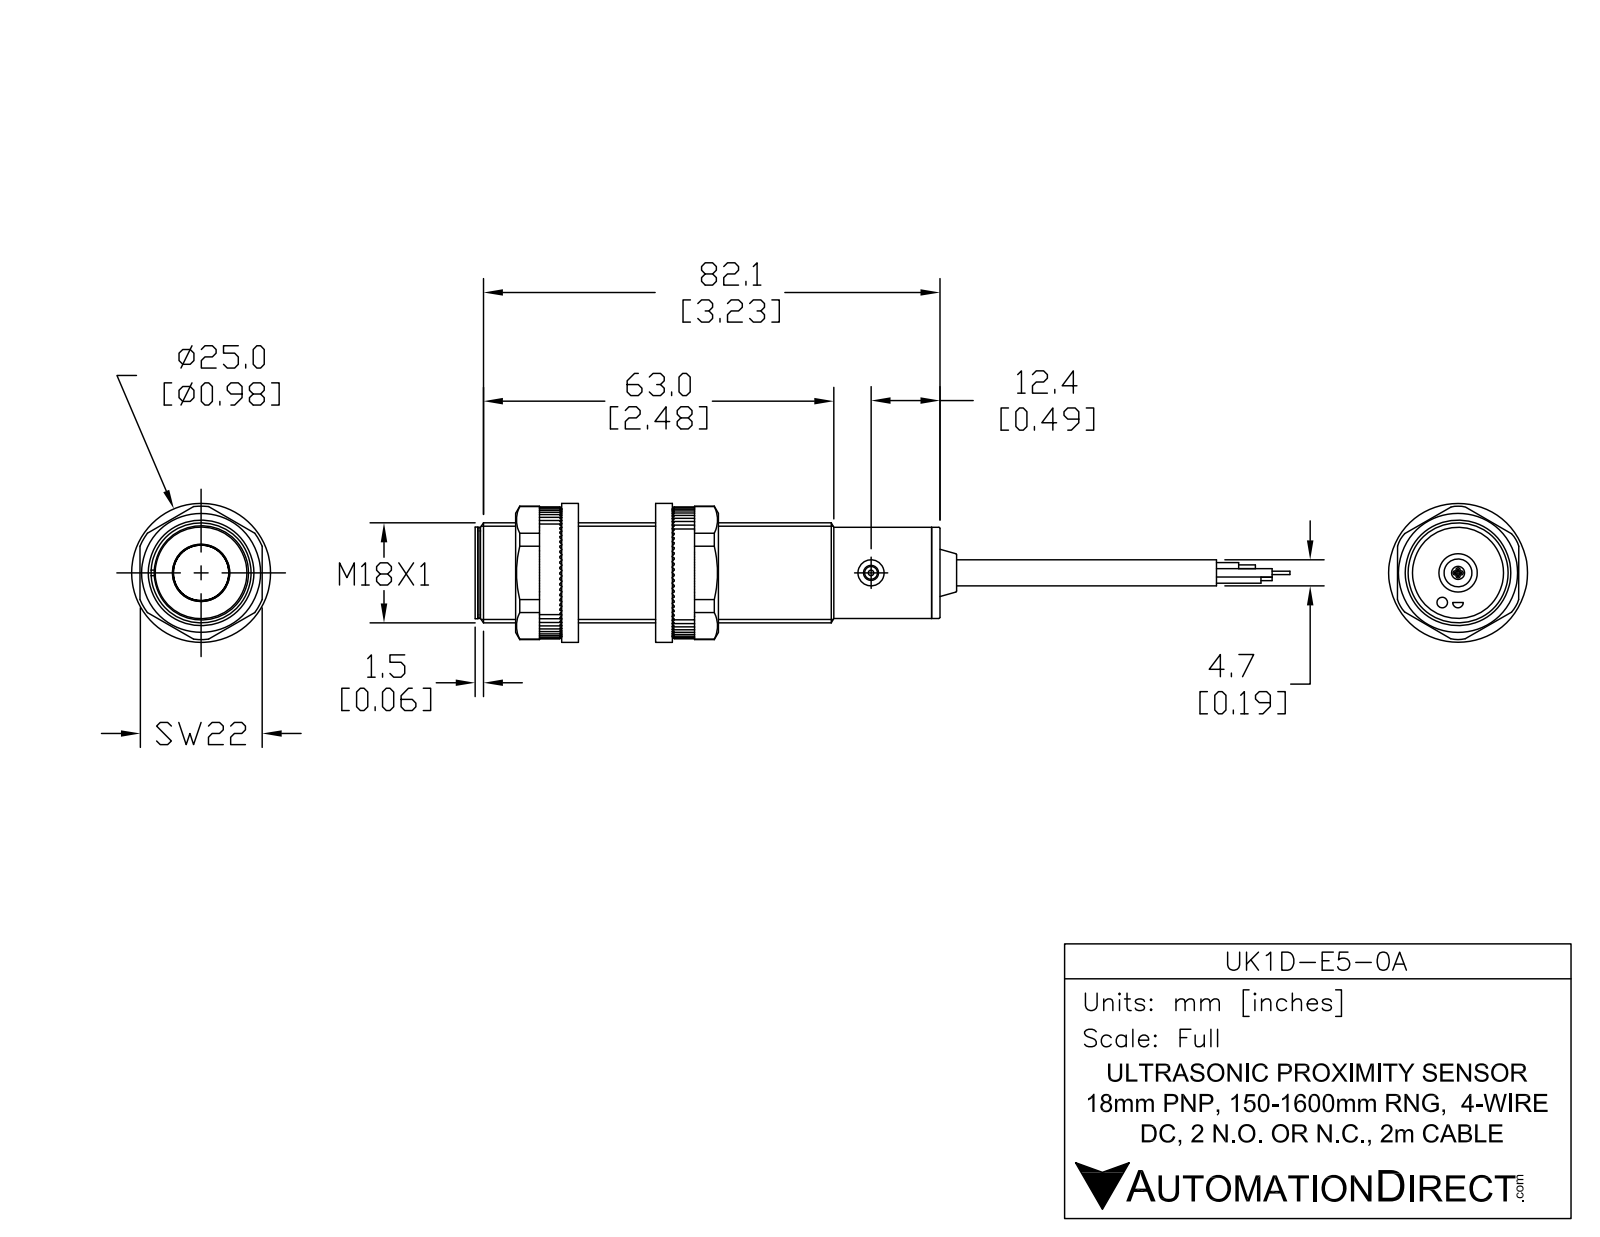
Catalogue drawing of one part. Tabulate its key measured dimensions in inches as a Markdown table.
| quantity | value |
| --- | --- |
| part name | UK1D-E5-0A |
| STEP written by | SolidWorks 2017 (AUTOMOTIVE_DESIGN) |
| units | inches |
| bodies | 6 solids, 55 faces (17 planar, 24 cylindrical, 14 other) |
| overall size | 4.832 × 0.709 × 0.709 |
| volume | 1.285 in³ |
| surface area | 10.69 in² |
| round holes (diameter × count) | 0.185 × 2, 0.106 × 1 |
| round bosses / shafts (diameter × count) | 0.709 × 1, 0.646 × 1, 0.622 × 1, 0.374 × 1, 0.189 × 1, 0.091 × 1 |
| main face-to-face distances | 3.193, 3.252, 0.059, 0.039, 3.232, 3.291, 0.041, 3.234, 3.293, 3.257 |
